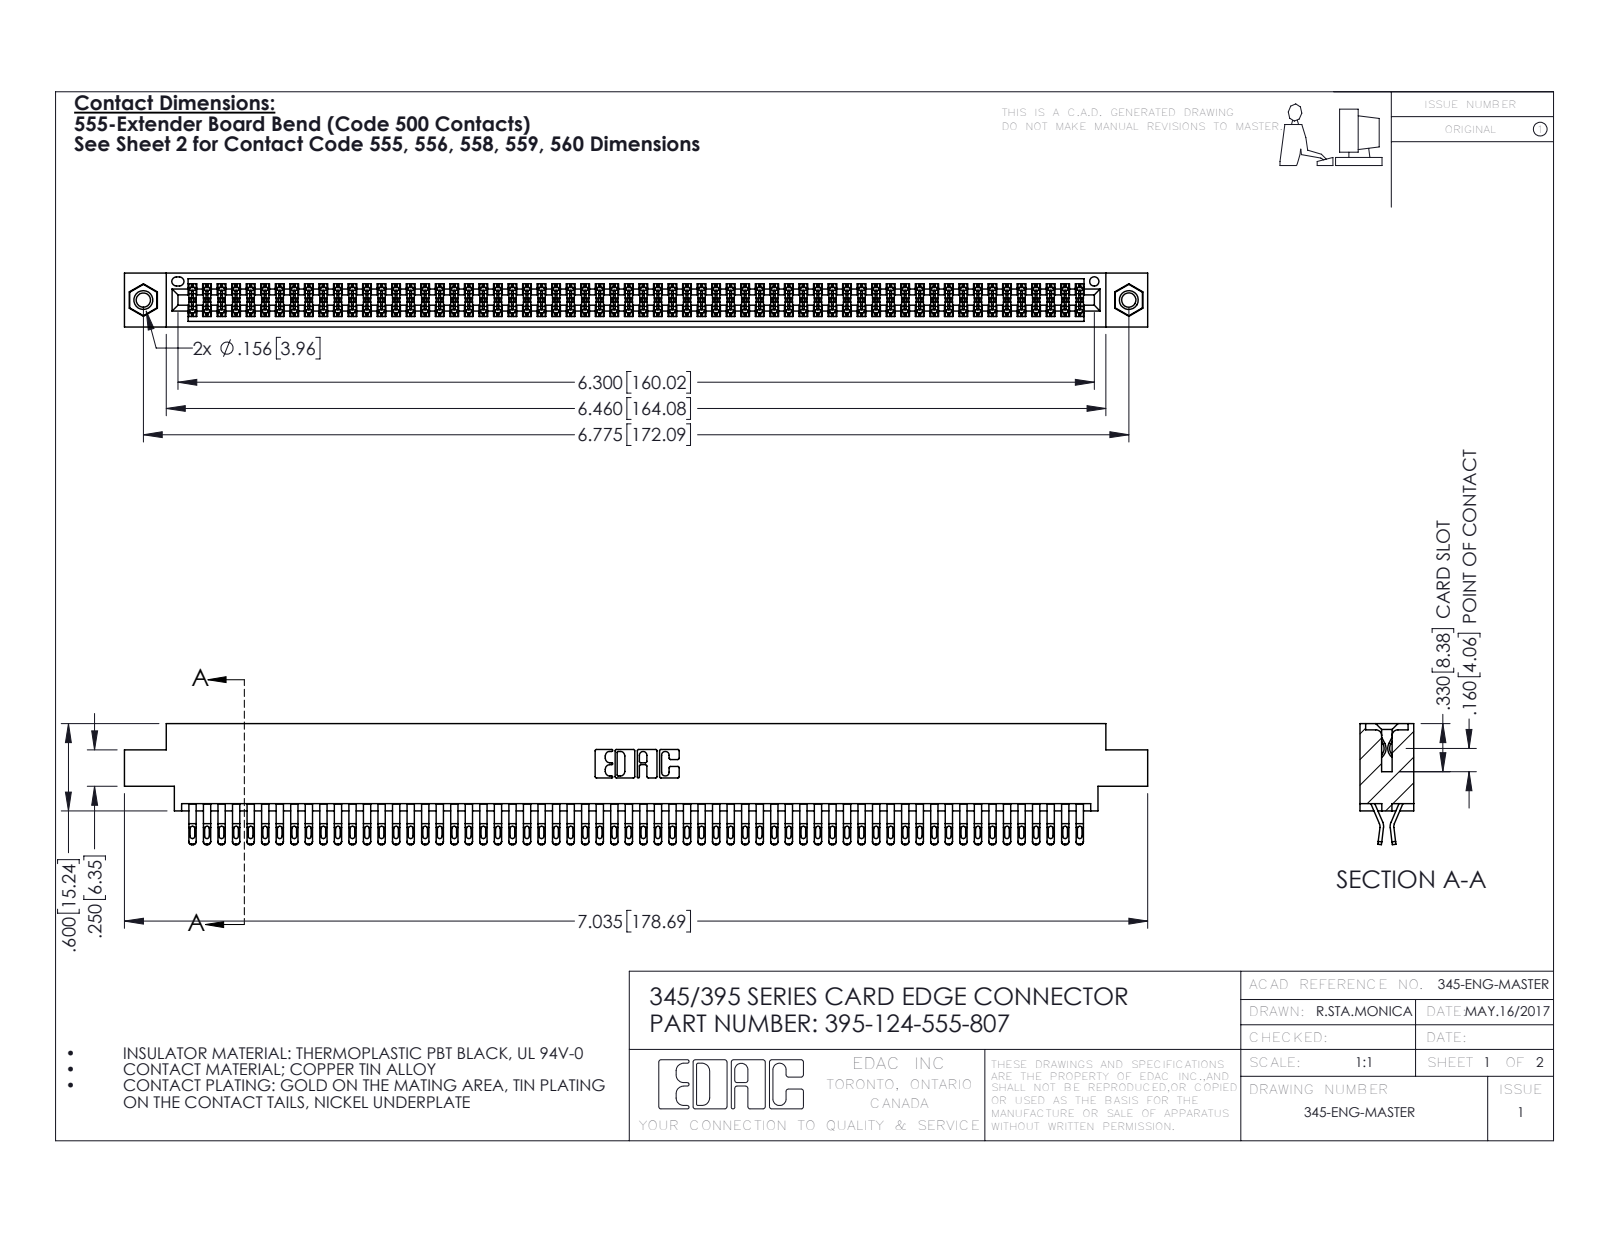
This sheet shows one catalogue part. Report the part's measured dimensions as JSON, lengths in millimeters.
{"part_name": "345-292-001_555 Tail; 345 Part_0.170 Offset - 0.156 Dia-TI; 345-250-001_345-250-005-103; 395-124-555-807", "step_written_by": "SolidWorks 2016 (CONFIG_CONTROL_DESIGN)", "units": "millimeters", "bodies": {"solids": 127, "faces": 7134, "planar": 3960, "cylindrical": 3158, "other": 16}, "overall_size": [178.7, 21.1, 9.4], "volume_mm3": 17780, "surface_area_mm2": 28080, "round_holes": [[2.5, 2], [3.2, 2], [4, 2], [1.6, 1]], "round_bosses_or_shafts": [[3.9, 2]], "partial_cylinders_radius": [[0.4, 310], [0.5, 248], [0.2, 186], [0.3, 22], [0.2, 6], [0.8, 6], [0.7, 3], [0.3, 2]], "face_to_face_distances": [1.8, 7.6, 0.6, 9.4, 5.1, 2.5, 6.9, 5.7, 4.4, 3.8], "hole_center_spacings": [6.9, 166.1, 172.1]}
